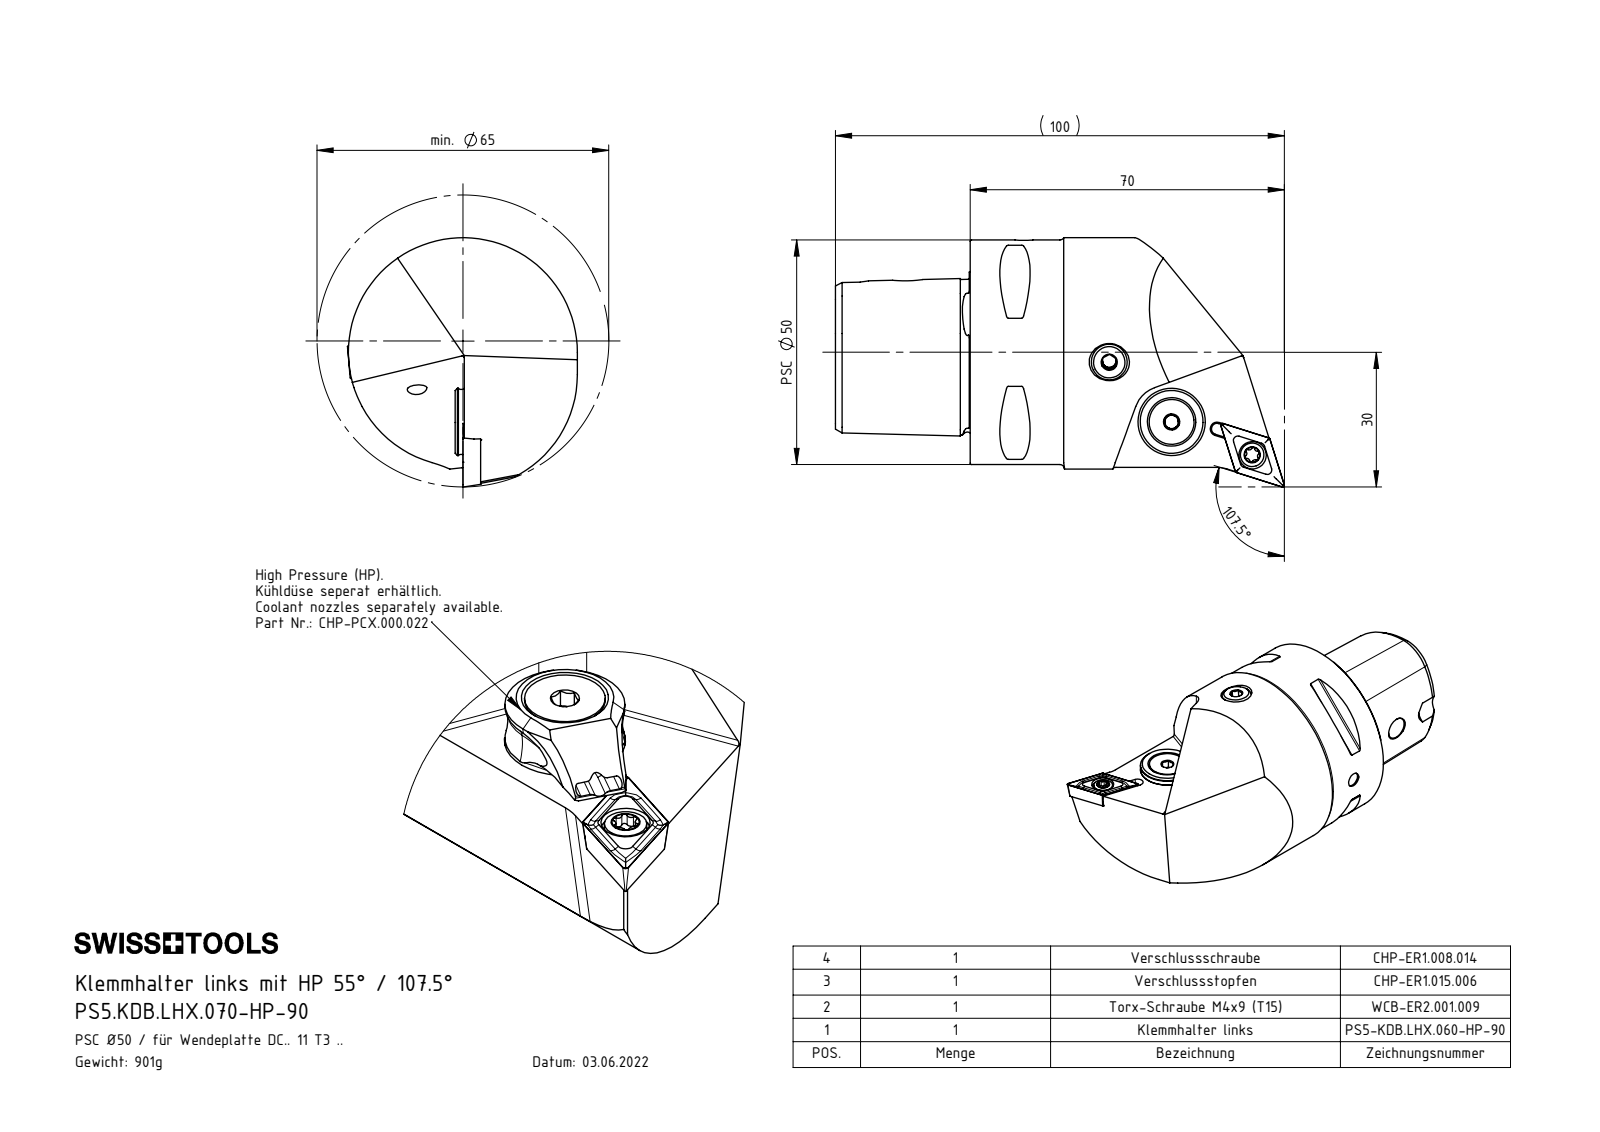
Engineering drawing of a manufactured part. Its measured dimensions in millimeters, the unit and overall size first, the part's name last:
Units: millimetres
Overall size (bounding box): 100.01 × 55.5 × 51.21
Round holes (diameter × count): ⌀4.2 ×3, ⌀6.1 ×2, ⌀1.2 ×1, ⌀2 ×1, ⌀2.5 ×1, ⌀3 ×1, ⌀3.3 ×1, ⌀4 ×1, ⌀4.4 ×1, ⌀5 ×1, ⌀5.2 ×1, ⌀7 ×1
Round bosses / shafts (diameter × count): ⌀50 ×1, ⌀15 ×1, ⌀13.4 ×1, ⌀10 ×1, ⌀8 ×1, ⌀5.5 ×1, ⌀5.25 ×1, ⌀5 ×1
Partial cylindrical surfaces — rounded edges, fillets, slot ends (radius × count): R0.5 ×10, R0.34 ×6, R0.59 ×6, R7 ×2, R25.5 ×2, R1.25 ×1, R4 ×1, R26 ×1
Main face-to-face distances: 30, 4.5, 20.7, 25.2, 19.18, 21.53, 0.83, 3.67, 44.4, 10
Hole centre spacings: 4.5, 5.61, 15.87, 15.99, 19.38, 19.5, 21.43, 21.56
Volume: 114 439 mm³ · Surface area: 23 502 mm²
Bodies: 8 solids, 389 faces (93 planar, 103 cylindrical, 193 other)
Part name (STEP PRODUCT): CHP-ER1.008.014_A; DIN 7991 - M5x15; CHP-ER1.015.006_A; B.L.X.070-HP-90 (+6 more)
STEP written by: SolidWorks 2017 (AUTOMOTIVE_DESIGN)
